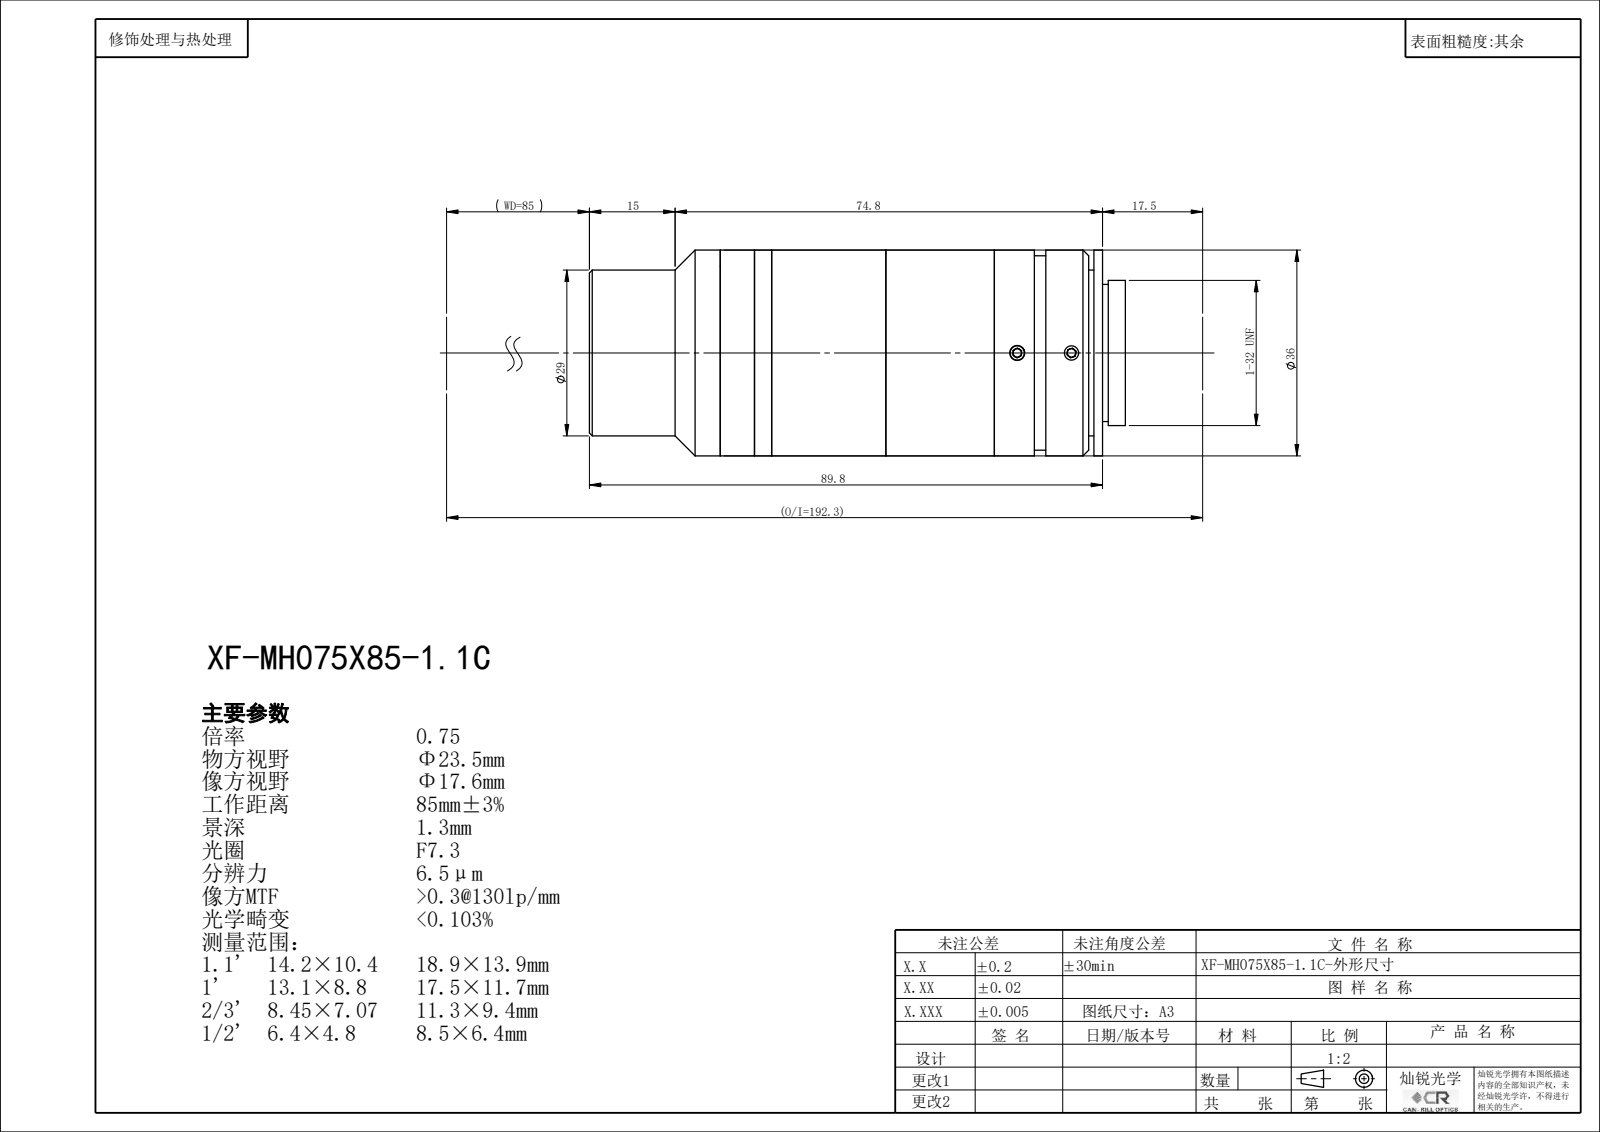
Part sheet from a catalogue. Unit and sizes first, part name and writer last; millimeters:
Units: millimetres
Overall size (bounding box): 93.83 × 36 × 36
Round holes (diameter × count): ⌀2.5 ×3, ⌀20 ×1, ⌀22.4 ×1, ⌀24 ×1, ⌀24.9 ×1, ⌀26 ×1, ⌀26.4 ×1
Round bosses / shafts (diameter × count): ⌀36 ×1, ⌀34 ×1, ⌀29 ×1, ⌀25.4 ×1
Main face-to-face distances: 18.93, 1.5, 17.43, 19, 36.43, 37.93, 20, 39, 56.43, 57.93
Bodies: 0 solids, 143 faces (70 planar, 44 cylindrical, 29 other)
Part name (STEP PRODUCT): XF-MH075X85-1.1C
STEP written by: SolidWorks 2022 (CONFIG_CONTROL_DESIGN)
